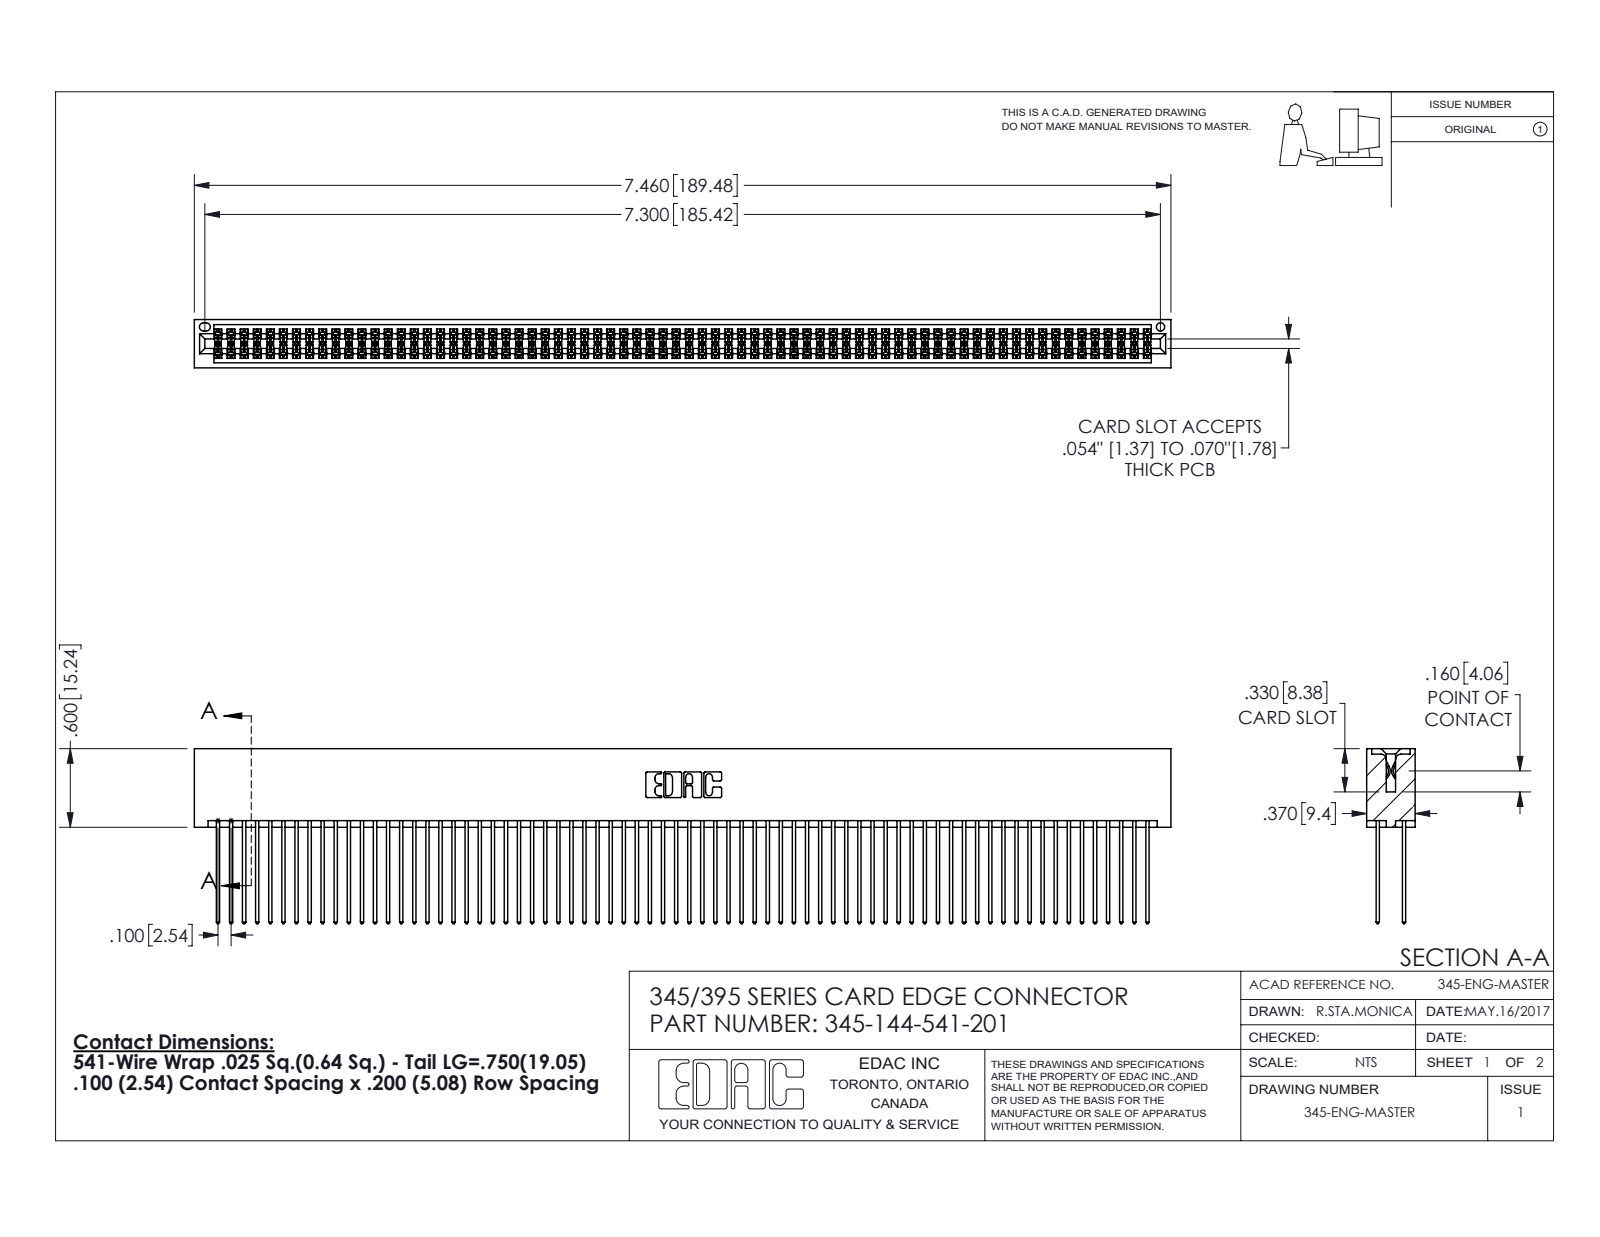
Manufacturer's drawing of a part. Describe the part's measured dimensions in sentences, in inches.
The part is named "345-144-541-201; 345-292-001_345-293-141; 345 Part_No Mounting Lugs". Its 3-D file was written by "SolidWorks 2016 (CONFIG_CONTROL_DESIGN)". It is 145 solids with 7318 faces: 4828 planar, 2490 cylindrical and 0 other. Overall it measures 7.46 by 1.337 by 0.37 inches. Its volume is 1.228 cubic inches and its surface area 53.5 square inches. Round holes: 1 of diameter 0.064. Partial cylindrical surfaces (rounded edges, fillets, slot ends): 216 of radius 0.006, 144 of radius 0.01, 22 of radius 0.01, 6 of radius 0.007, 6 of radius 0.031, 3 of radius 0.026, 2 of radius 0.014, 2 of radius 0.019. The main face-to-face distances are 0.298, 0.072, 0.2, 0.098, 0.272, 0.025, 0.225, 0.37, 0.175, 0.149.
